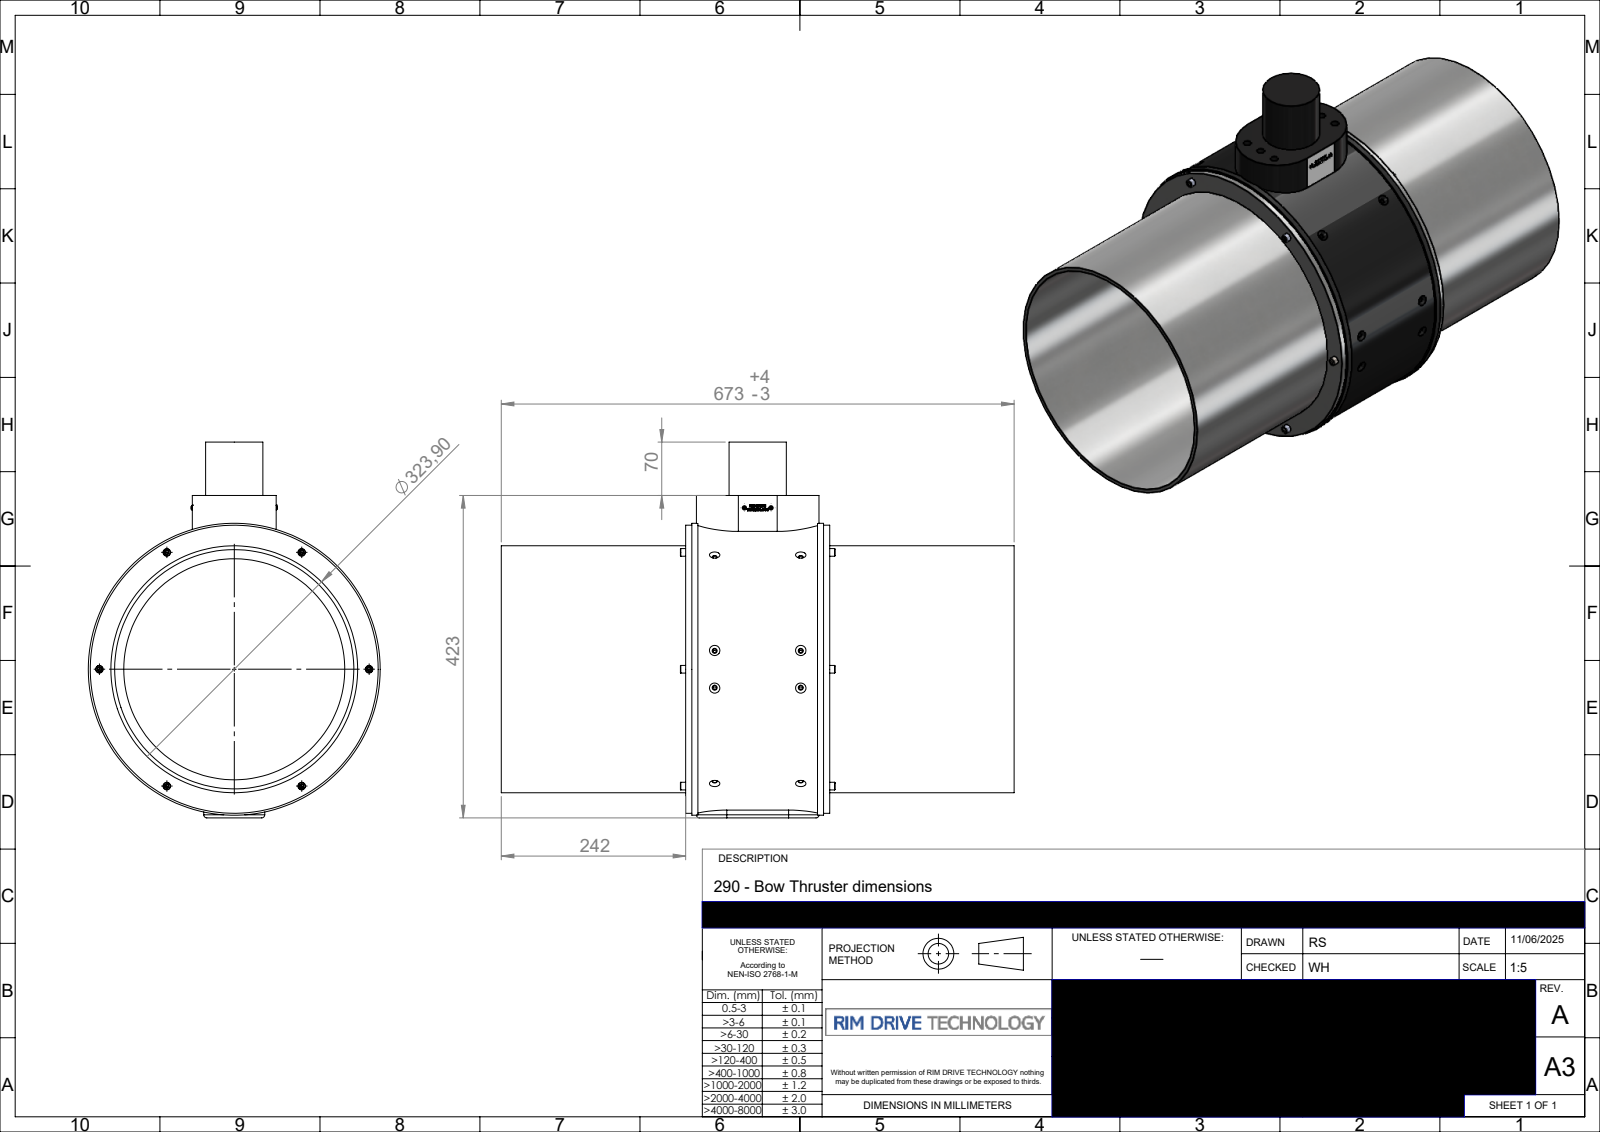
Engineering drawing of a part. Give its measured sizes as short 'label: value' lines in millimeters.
name: P-290-030-rev-A-BT
written by: SolidWorks 2024 (AUTOMOTIVE_DESIGN)
unit: mm
bodies: 1 solid, 859 faces (597 planar, 64 cylindrical, 198 other)
size: 673 × 493 × 383
volume: 11 880 000 mm³; area: 1 525 000 mm²
holes: 16× ⌀5, 6× ⌀10.2, 2× ⌀3.5, 1× ⌀290, 1× ⌀313.9
bosses: 6× ⌀10, 2× ⌀11.57, 2× ⌀5.7, 1× ⌀383, 1× ⌀378, 1× ⌀323.9, 1× ⌀75
rounds: 2× R4, 2× R40, 2× R55
face distances: 189, 423, 8, 175, 14, 13.95, 161.05, 175.05, 242, 431
hole spacings: 113, 0.36, 25, 115.73, 50, 123.57, 35
